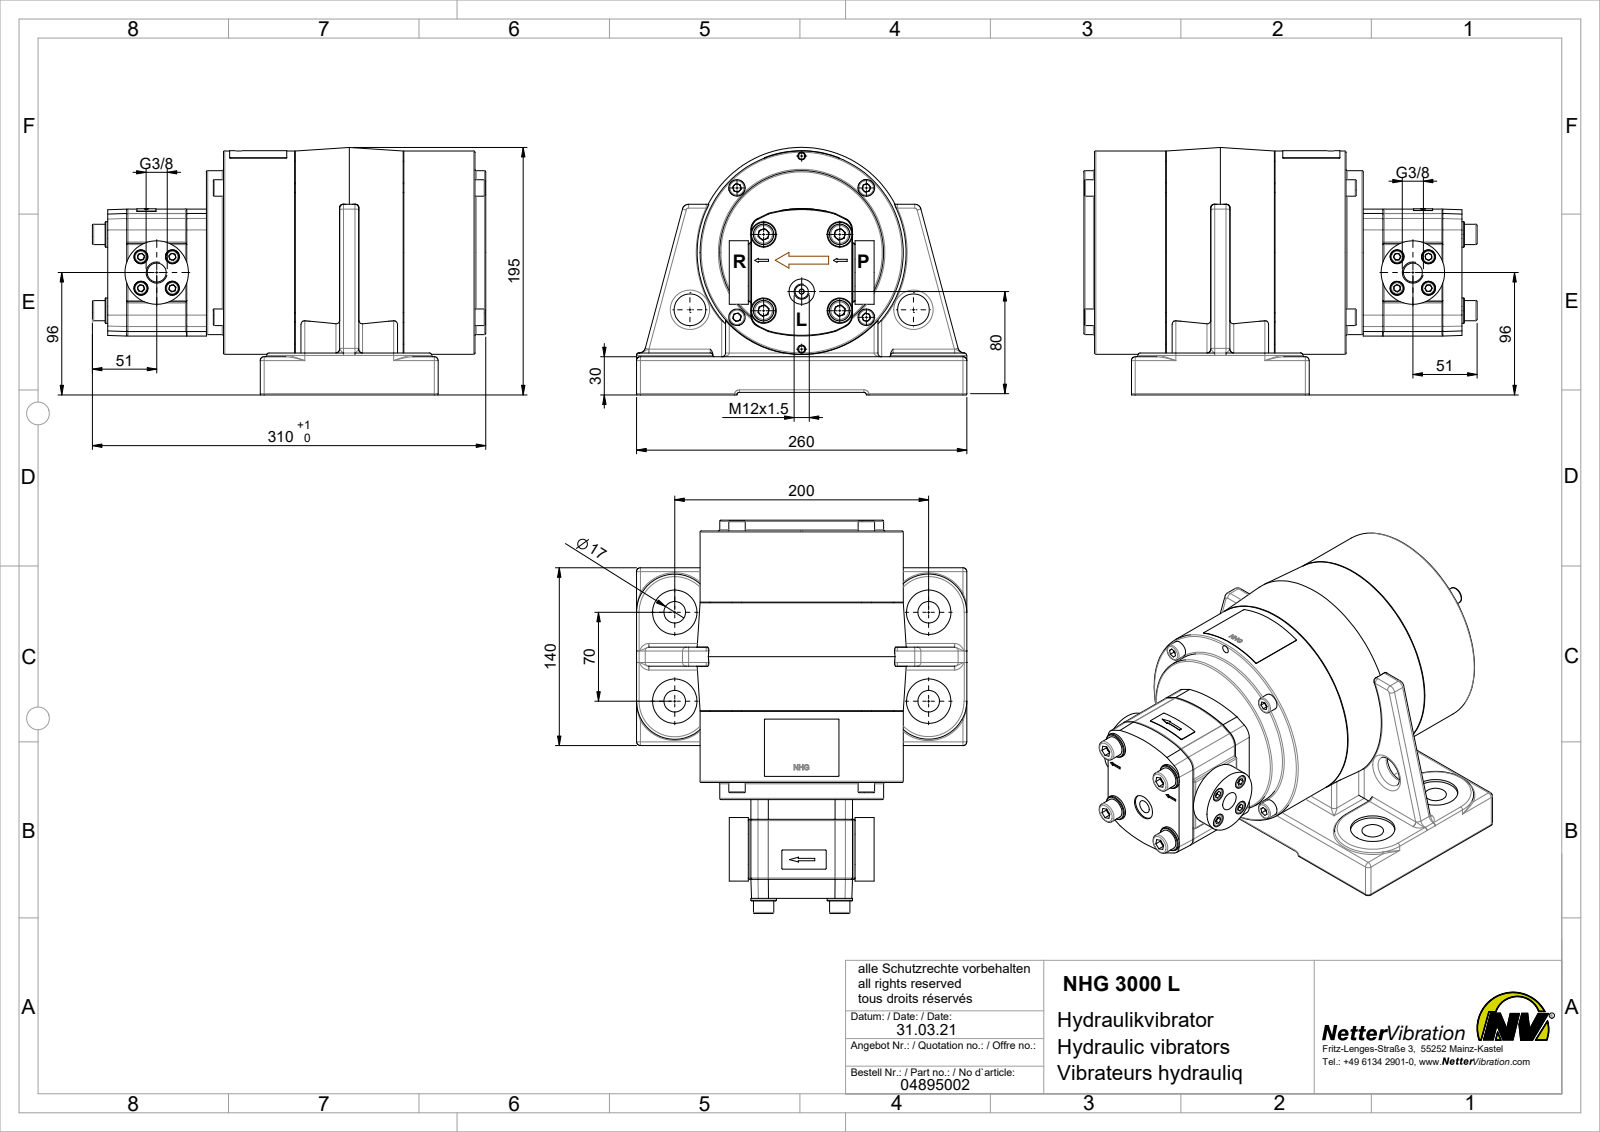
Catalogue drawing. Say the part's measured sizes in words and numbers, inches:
The part is named "NHG 3000L #04895002". Its 3-D file was written by "SolidWorks 2023 (AUTOMOTIVE_DESIGN)". It is 14 solids with 1434 faces: 555 planar, 454 cylindrical and 425 other. Overall it measures 12.035 by 10.236 by 7.559 inches. Its volume is 266.5 cubic inches and its surface area 792.4 square inches. Round holes: 13 of diameter 0.433, 12 of diameter 0.197, 8 of diameter 0.256, 4 of diameter 0.268, 4 of diameter 0.335, 4 of diameter 0.354, 4 of diameter 0.394, 4 of diameter 0.669, 4 of diameter 0.709, 4 of diameter 1.378, 2 of diameter 0.244, 2 of diameter 0.984. Round bosses or shafts: 12 of diameter 0.394, 10 of diameter 0.236, 4 of diameter 0.63, 4 of diameter 0.512, 4 of diameter 0.315, 1 of diameter 6.299, 1 of diameter 5.079, 1 of diameter 5.039. Partial cylindrical surfaces (rounded edges, fillets, slot ends): 34 of radius 0.118, 28 of radius 0.039, 8 of radius 0.079, 6 of radius 0.197, 4 of radius 0.394, 4 of radius 1.181, 2 of radius 3.937. The main face-to-face distances are 4.429, 0.787, 0.079, 0.295, 1.909, 0.65, 5.551, 0.433, 3.642, 4.724. The hole center spacings are 1.046, 0.098, 0.689, 0.787, 0.974, 1.113, 1.476, 2.1.
